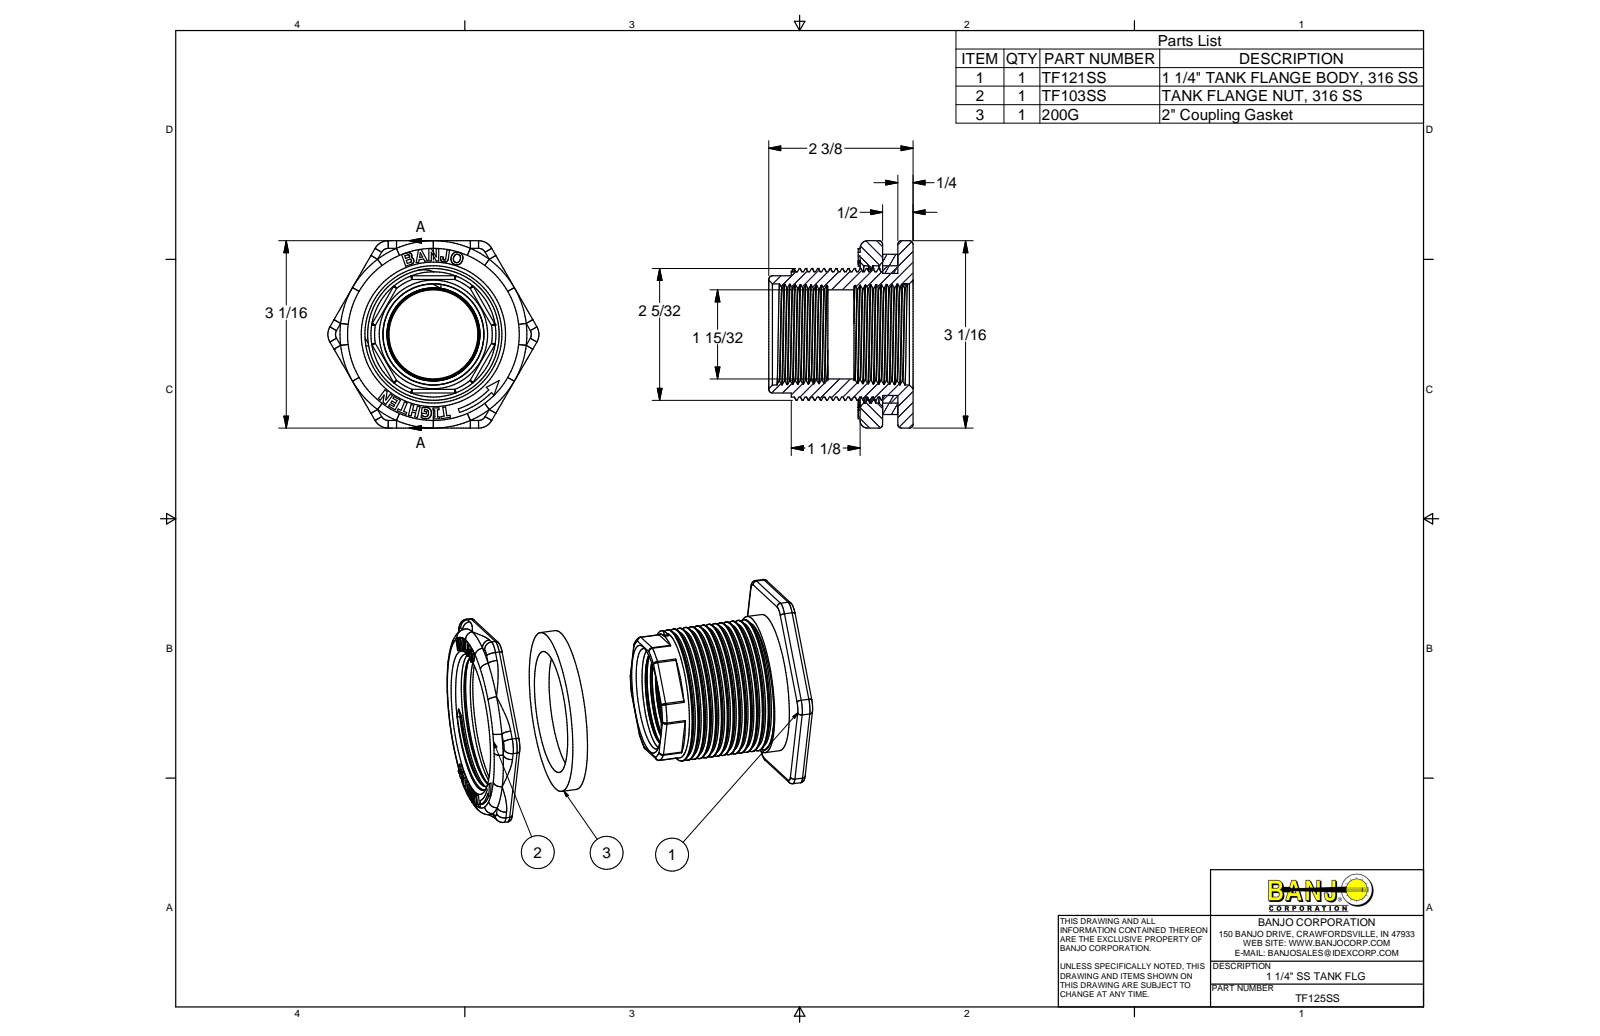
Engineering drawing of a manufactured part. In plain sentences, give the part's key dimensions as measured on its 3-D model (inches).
The part is named "TF125SS; TF121SS; TF103SS; 200G". Its 3-D file was written by "Autodesk Inventor 2013 (AUTOMOTIVE_DESIGN)". It is 3 solids with 396 faces: 173 planar, 72 cylindrical and 151 other. Overall it measures 3.468 by 3.07 by 2.37 inches. Its volume is 7.186 cubic inches and its surface area 74.66 square inches. Round holes: 1 of diameter 1.46, 1 of diameter 2, 1 of diameter 2.142, 1 of diameter 2.25. Round bosses or shafts: 1 of diameter 2.625, 1 of diameter 2.16, 1 of diameter 2.052. Partial cylindrical surfaces (rounded edges, fillets, slot ends): 36 of radius 0.06, 6 of radius 0.125, 6 of radius 0.25, 1 of radius 0.4, 1 of radius 1.286, 1 of radius 1.349. The main face-to-face distances are 0.25, 0.5, 0.37, 0.62, 0.87, 0.575, 2.495, 3.07, 1.92, 0.9.
